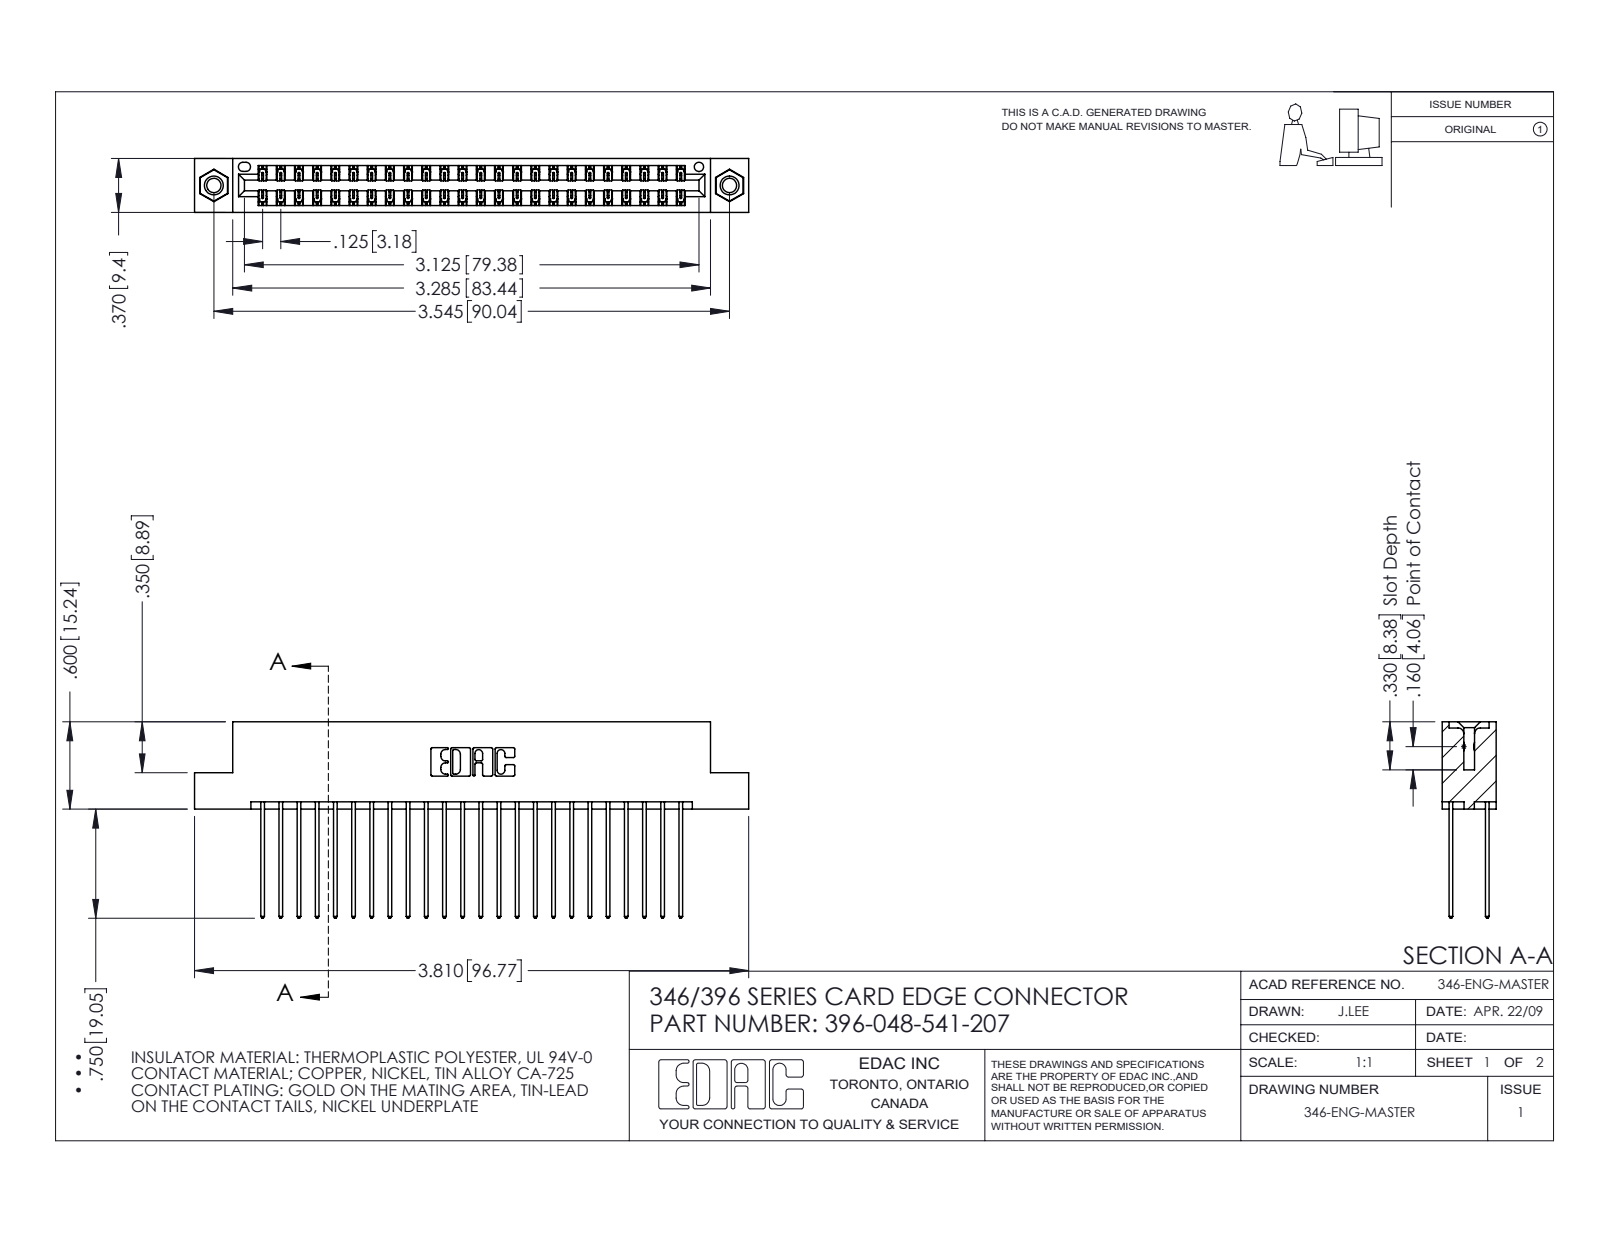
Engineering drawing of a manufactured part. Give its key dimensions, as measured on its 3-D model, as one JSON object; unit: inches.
{"part_name": "346 Part_Flush Mounting Lugs - 0.156 Dia-TI; 396-048-541-207; 345-250-001_345-250-005-103; 345-292-001_345-293-141", "step_written_by": "SolidWorks 2016 (CONFIG_CONTROL_DESIGN)", "units": "inches", "bodies": {"solids": 51, "faces": 2678, "planar": 1788, "cylindrical": 874, "other": 16}, "overall_size": [3.81, 1.35, 0.37], "volume_in3": 0.583, "surface_area_in2": 22.03, "round_holes": [[0.098, 2], [0.125, 2], [0.156, 2], [0.064, 1]], "round_bosses_or_shafts": [[0.155, 2]], "partial_cylinders_radius": [[0.006, 72], [0.01, 48], [0.01, 22], [0.007, 6], [0.031, 6], [0.026, 3], [0.014, 2], [0.022, 2]], "face_to_face_distances": [0.048, 0.322, 0.25, 0.072, 0.298, 0.025, 0.37, 0.275, 0.225, 0.148], "hole_center_spacings": [0.246, 3.337, 3.545]}
